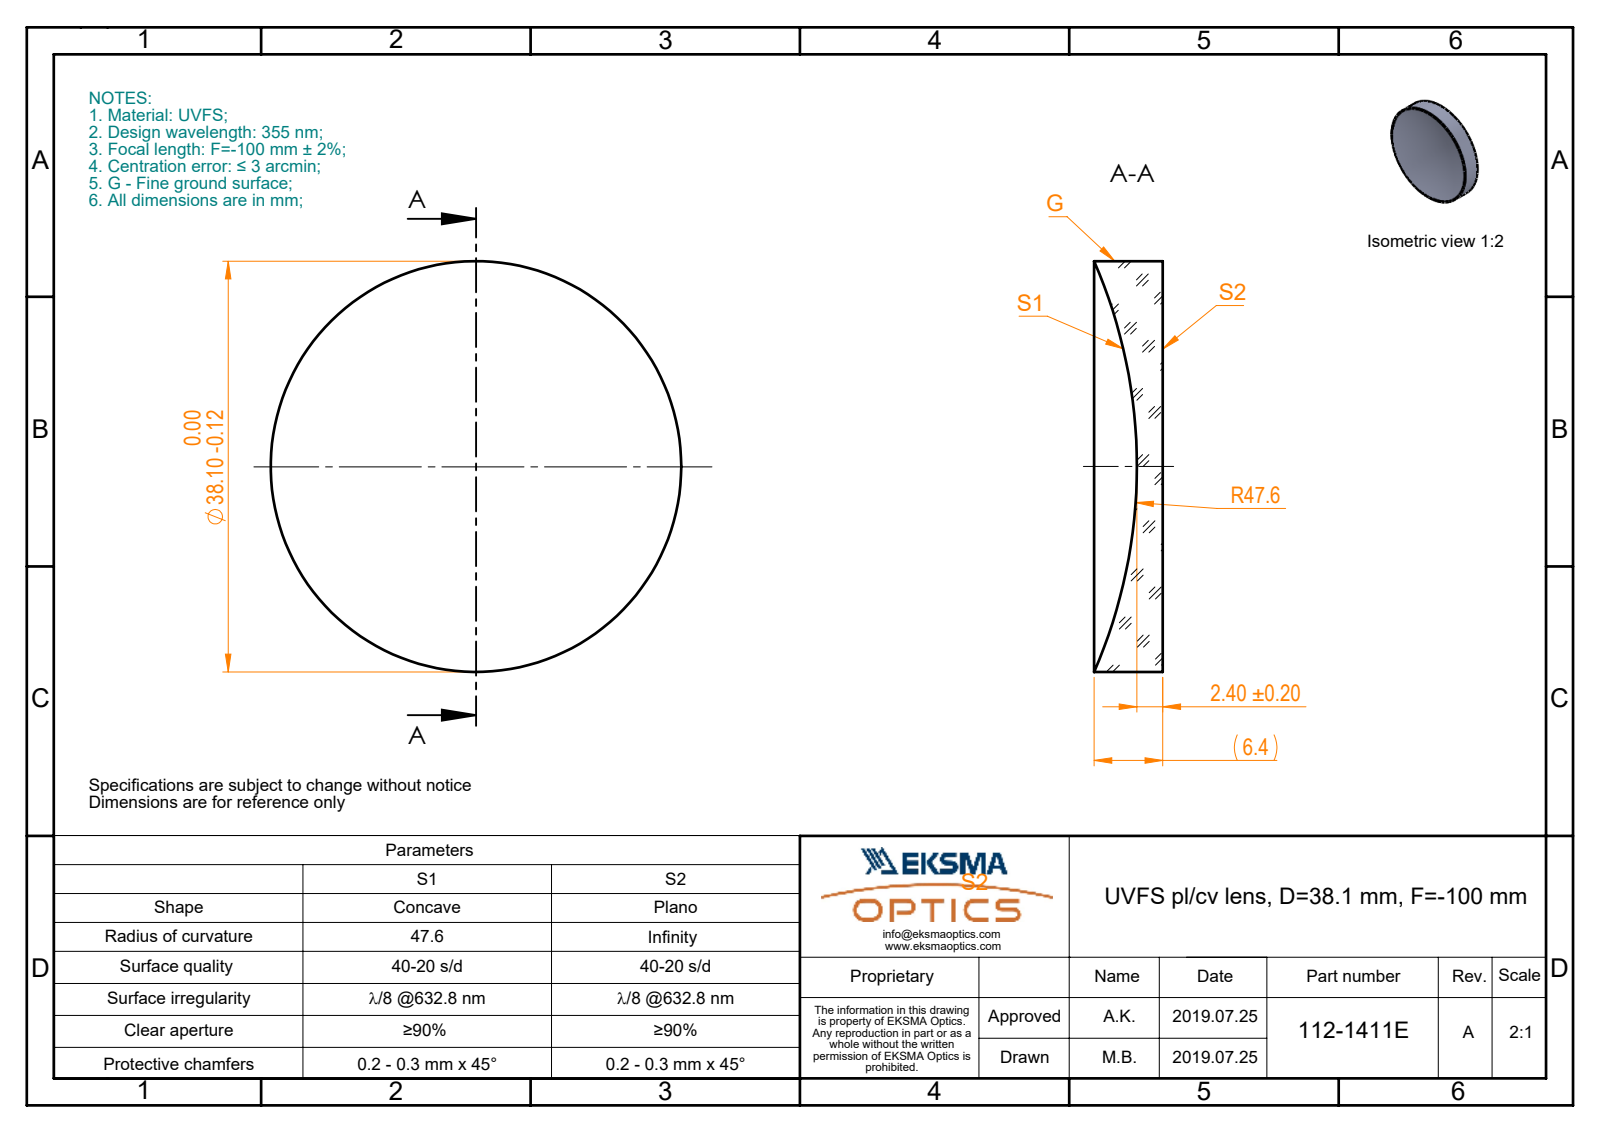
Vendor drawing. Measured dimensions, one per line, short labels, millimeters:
name: 112-1411E UVFS pl-cv 38.1 F-100
written by: SolidWorks 2017 (CONFIG_CONTROL_DESIGN)
unit: mm
bodies: 1 solid, 5 faces (1 planar, 2 cylindrical, 2 other)
size: 38.1 × 38.1 × 6.38
volume: 4 971 mm³; area: 3 093 mm²
bosses: 1× ⌀38.1
